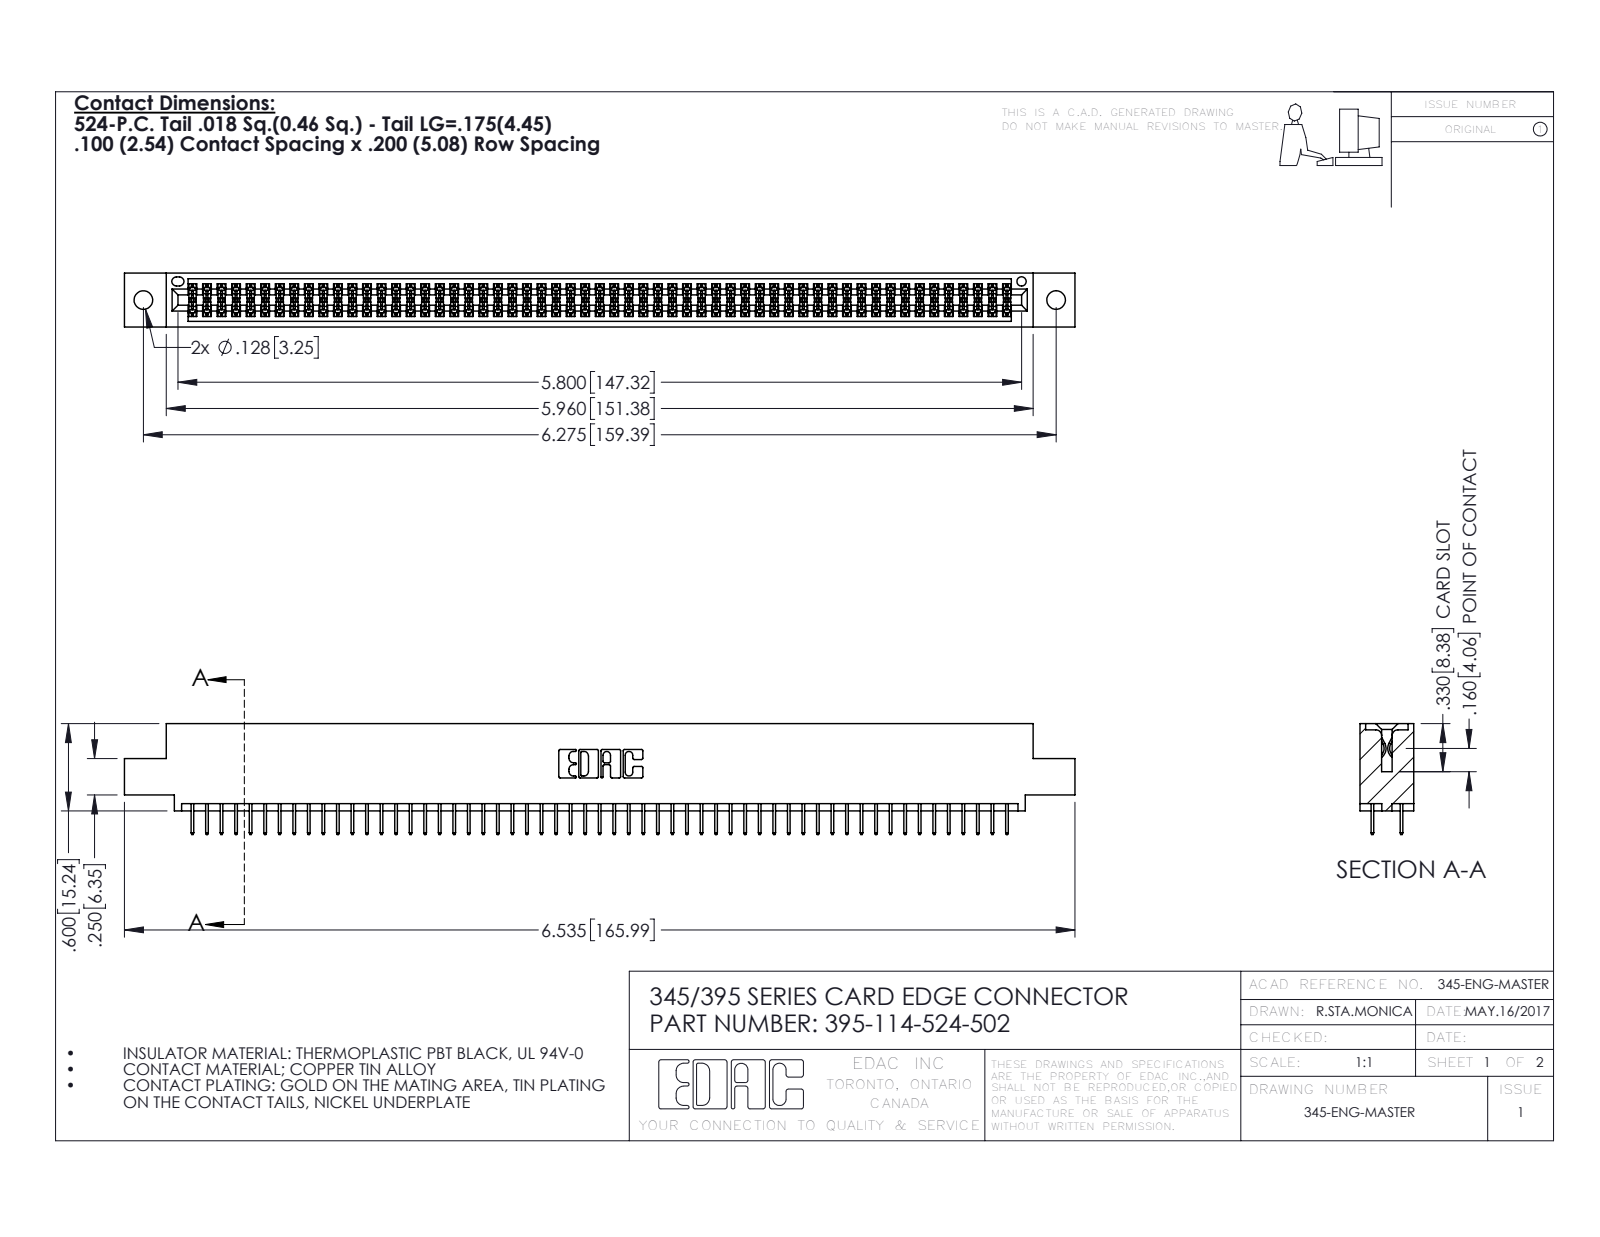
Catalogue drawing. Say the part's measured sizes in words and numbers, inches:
The part is named "345-292-001_345-293-124; 395-114-524-502; 345 Part_0.110 Offset - 0.128 Dia". Its 3-D file was written by "SolidWorks 2016 (CONFIG_CONTROL_DESIGN)". It is 115 solids with 6286 faces: 4530 planar, 1756 cylindrical and 0 other. Overall it measures 6.535 by 0.762 by 0.37 inches. Its volume is 0.975 cubic inches and its surface area 36.08 square inches. Round holes: 2 of diameter 0.128, 1 of diameter 0.064. Partial cylindrical surfaces (rounded edges, fillets, slot ends): 171 of radius 0.006, 22 of radius 0.01, 6 of radius 0.007, 6 of radius 0.031, 3 of radius 0.026, 2 of radius 0.014, 2 of radius 0.019, 2 of radius 0.022. The main face-to-face distances are 0.072, 0.298, 0.2, 0.37, 0.098, 0.272, 0.025, 0.225, 0.072, 0.175. The hole center spacings are 0.27, 6.039, 6.275.
